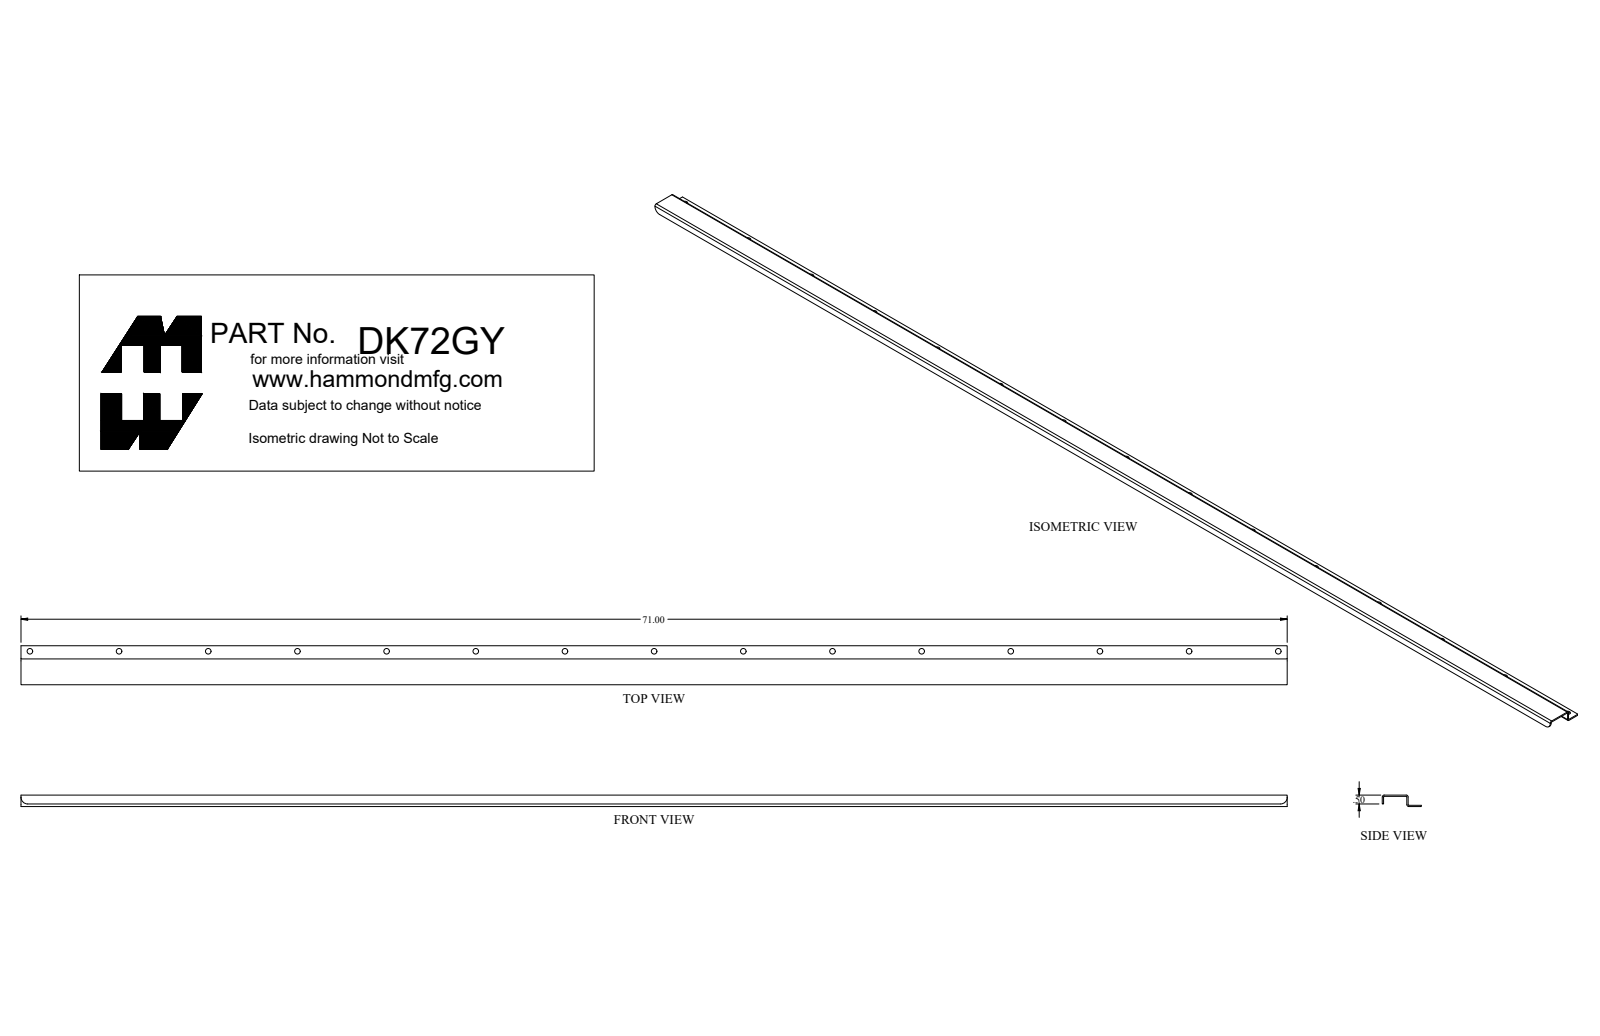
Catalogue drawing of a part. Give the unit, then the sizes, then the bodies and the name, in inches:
Units: inches
Overall size (bounding box): 71 × 2.188 × 1.322
Round holes (diameter × count): ⌀0.313 ×15, ⌀0.201 ×1, ⌀0.275 ×1
Round bosses / shafts (diameter × count): ⌀0.625 ×1, ⌀0.483 ×1, ⌀0.25 ×1
Partial cylindrical surfaces — rounded edges, fillets, slot ends (radius × count): R0.036 ×3, R0.108 ×3, R0.375 ×2
Main face-to-face distances: 0.072, 0.572, 0.644, 1.376, 0.5, 0.063, 0.635, 0.707, 0.135, 1.448
Hole centre spacings: 5, 10, 15, 20, 25, 30, 35, 40
Volume: 19.2 in³ · Surface area: 567 in²
Bodies: 5 solids, 89 faces (35 planar, 48 cylindrical, 6 other)
Part name (STEP PRODUCT): DK72GY_Default
STEP written by: SolidWorks 2018 (CONFIG_CONTROL_DESIGN)
